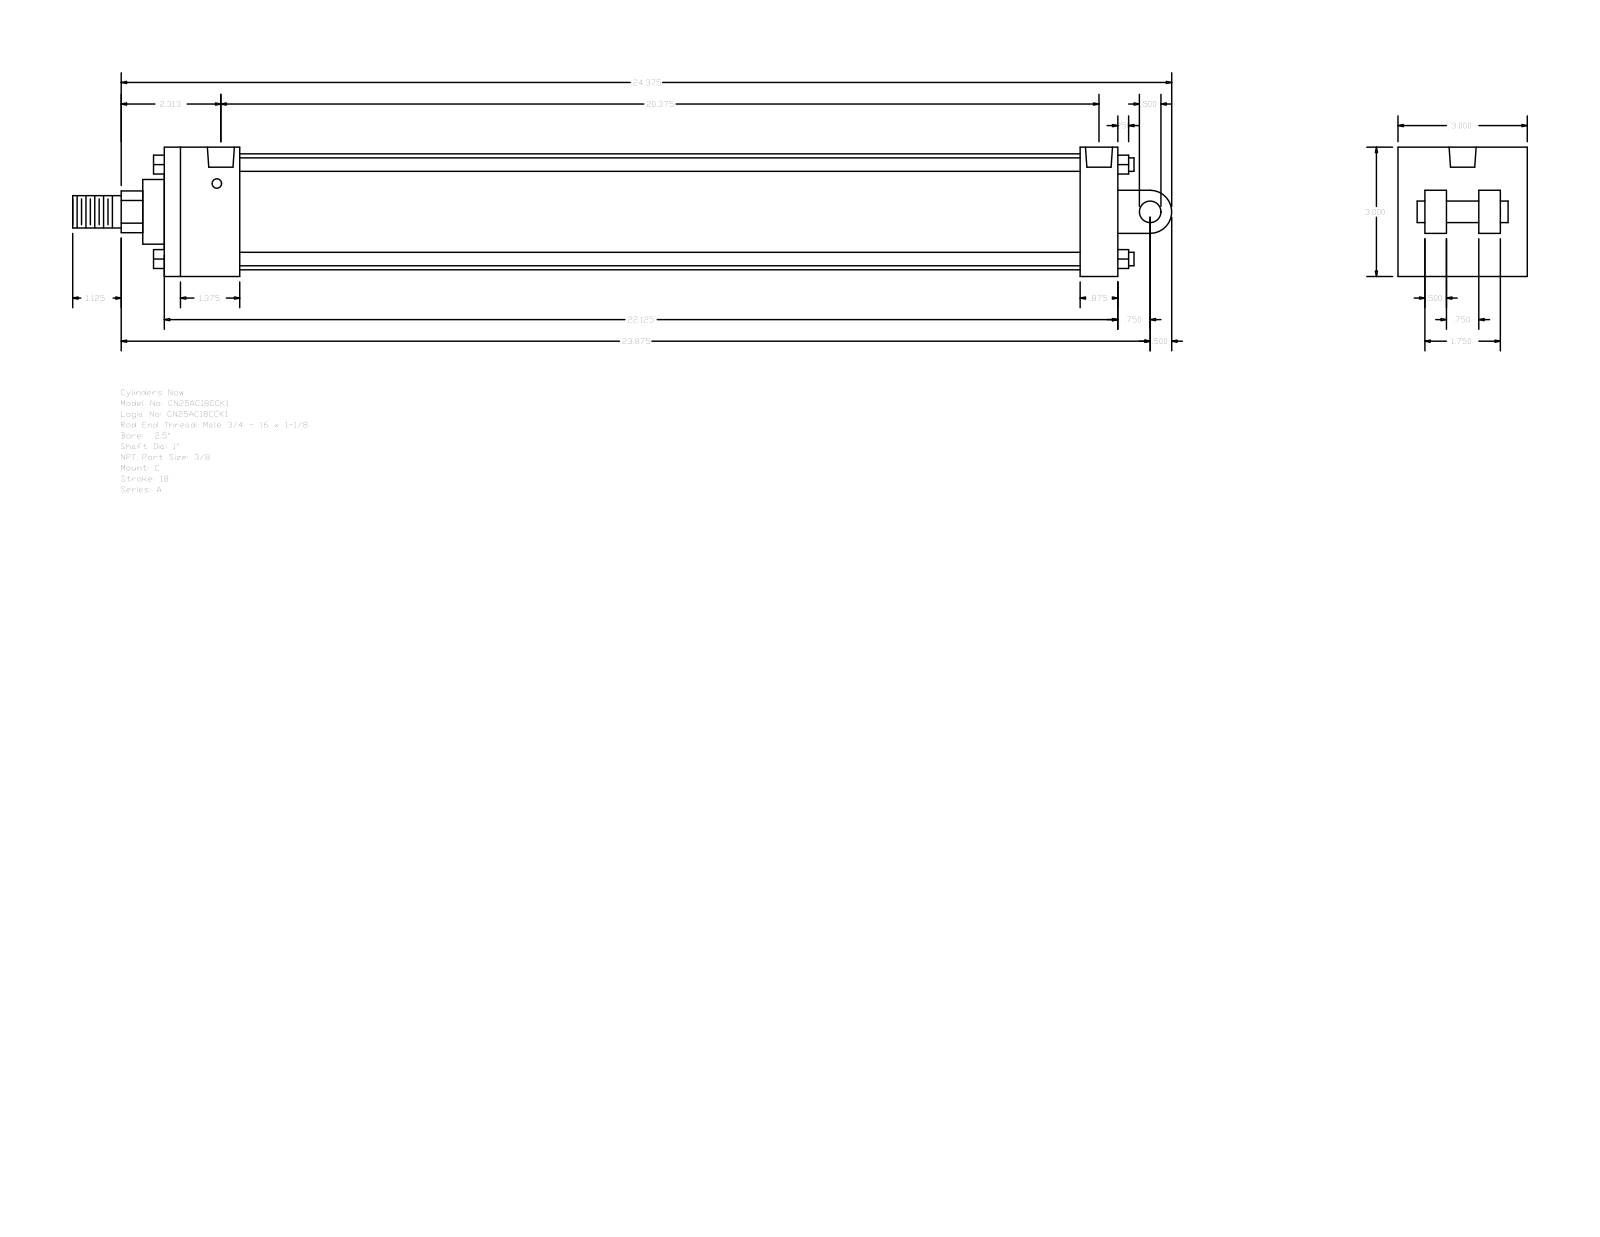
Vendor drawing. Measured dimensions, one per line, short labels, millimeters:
name: A_C__0250_1
written by: GSSL Pune (CONFIG_CONTROL_DESIGN)
unit: mm
bodies: 0 solids, 135 faces (102 planar, 33 cylindrical, 0 other)
size: 647.7 × 76.2 × 76.2
holes: 4× ⌀5.56, 2× ⌀15.93
bosses: 4× ⌀7.94, 1× ⌀68.33, 1× ⌀38.1, 1× ⌀25.4, 1× ⌀19.05, 1× ⌀12.7
rounds: 1× R12.29, 1× R12.7
face distances: 76.2, 561.98, 12.7, 44.45, 539.75, 495.3, 517.53, 22.23, 15.87, 25.4
hole spacings: 2.38, 519.9, 522.28, 517.52
